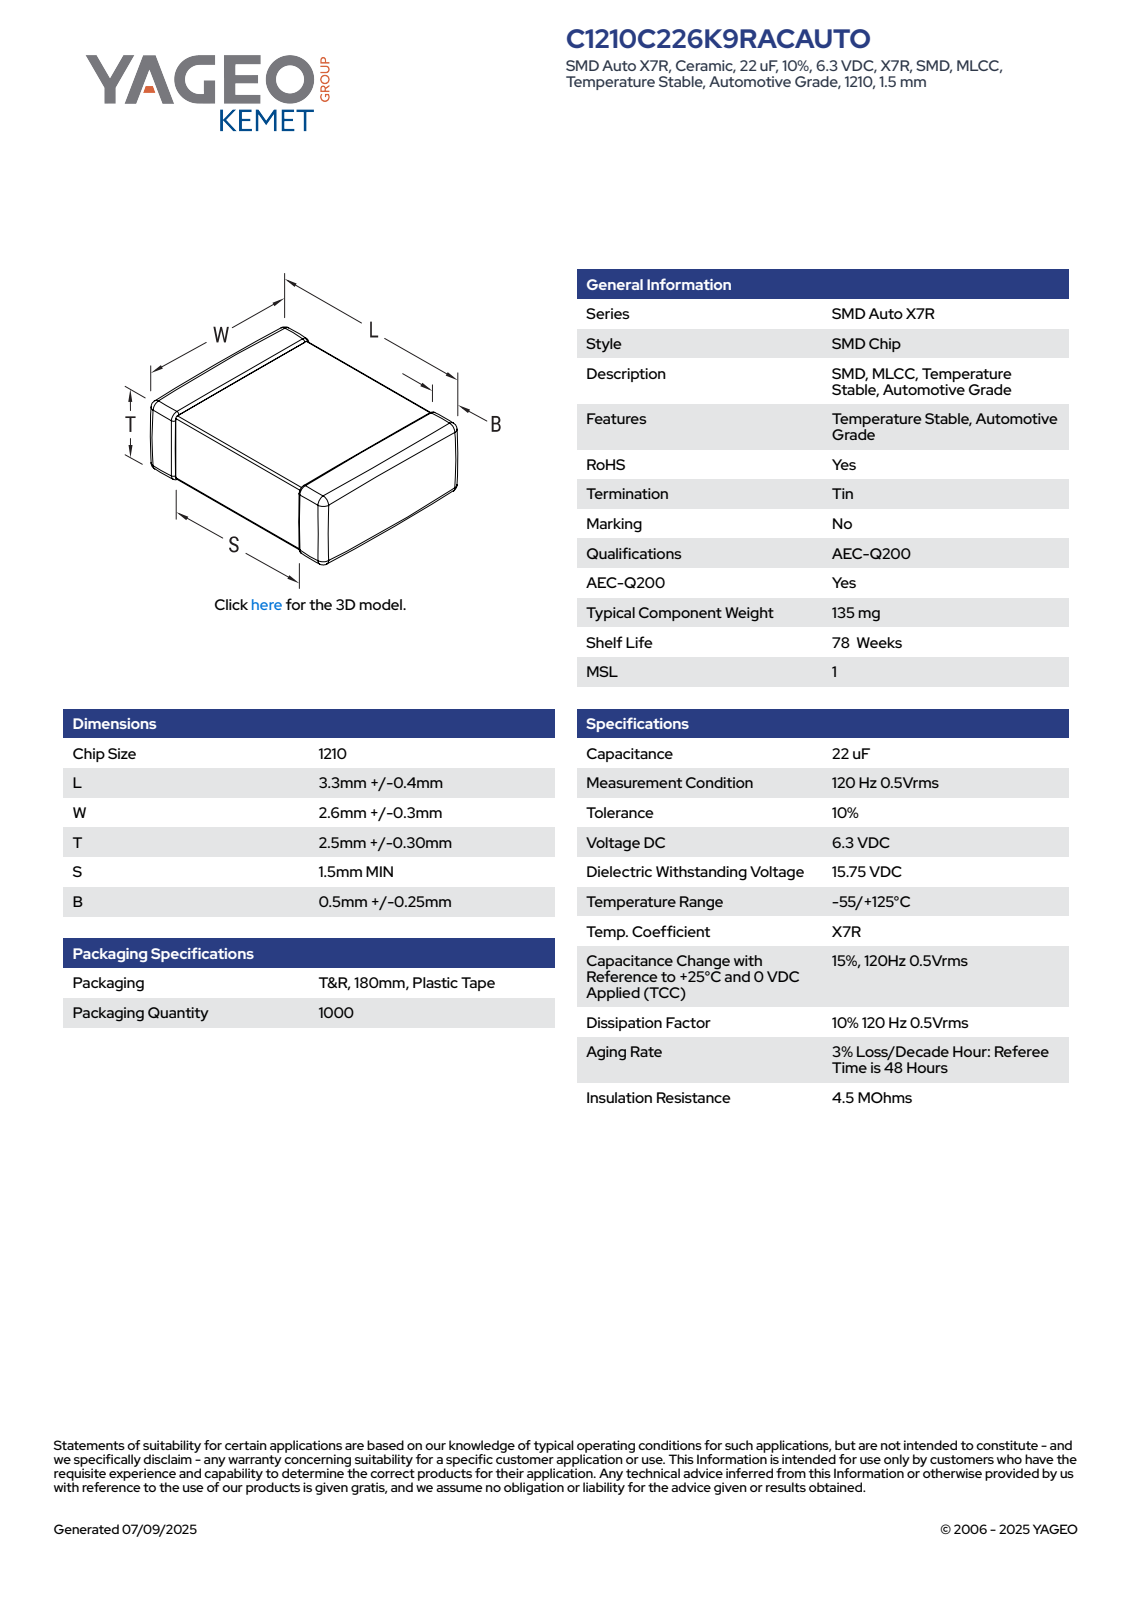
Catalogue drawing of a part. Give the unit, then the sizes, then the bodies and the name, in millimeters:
Units: millimetres
Overall size (bounding box): 3.7 × 2.9 × 2.8
Main face-to-face distances: 3.7, 2.74, 2.84, 2.68, 2.78, 2.8, 2.9, 0.43, 1.57, 2.13
Volume: 29 mm³ · Surface area: 58 mm²
Bodies: 4 solids, 125 faces (71 planar, 38 cylindrical, 16 other)
Part name (STEP PRODUCT): CCS_CCSTD_1210_L3.7W2.9T2.8B0.5
STEP written by: SolidWorks 2021 (AUTOMOTIVE_DESIGN)
